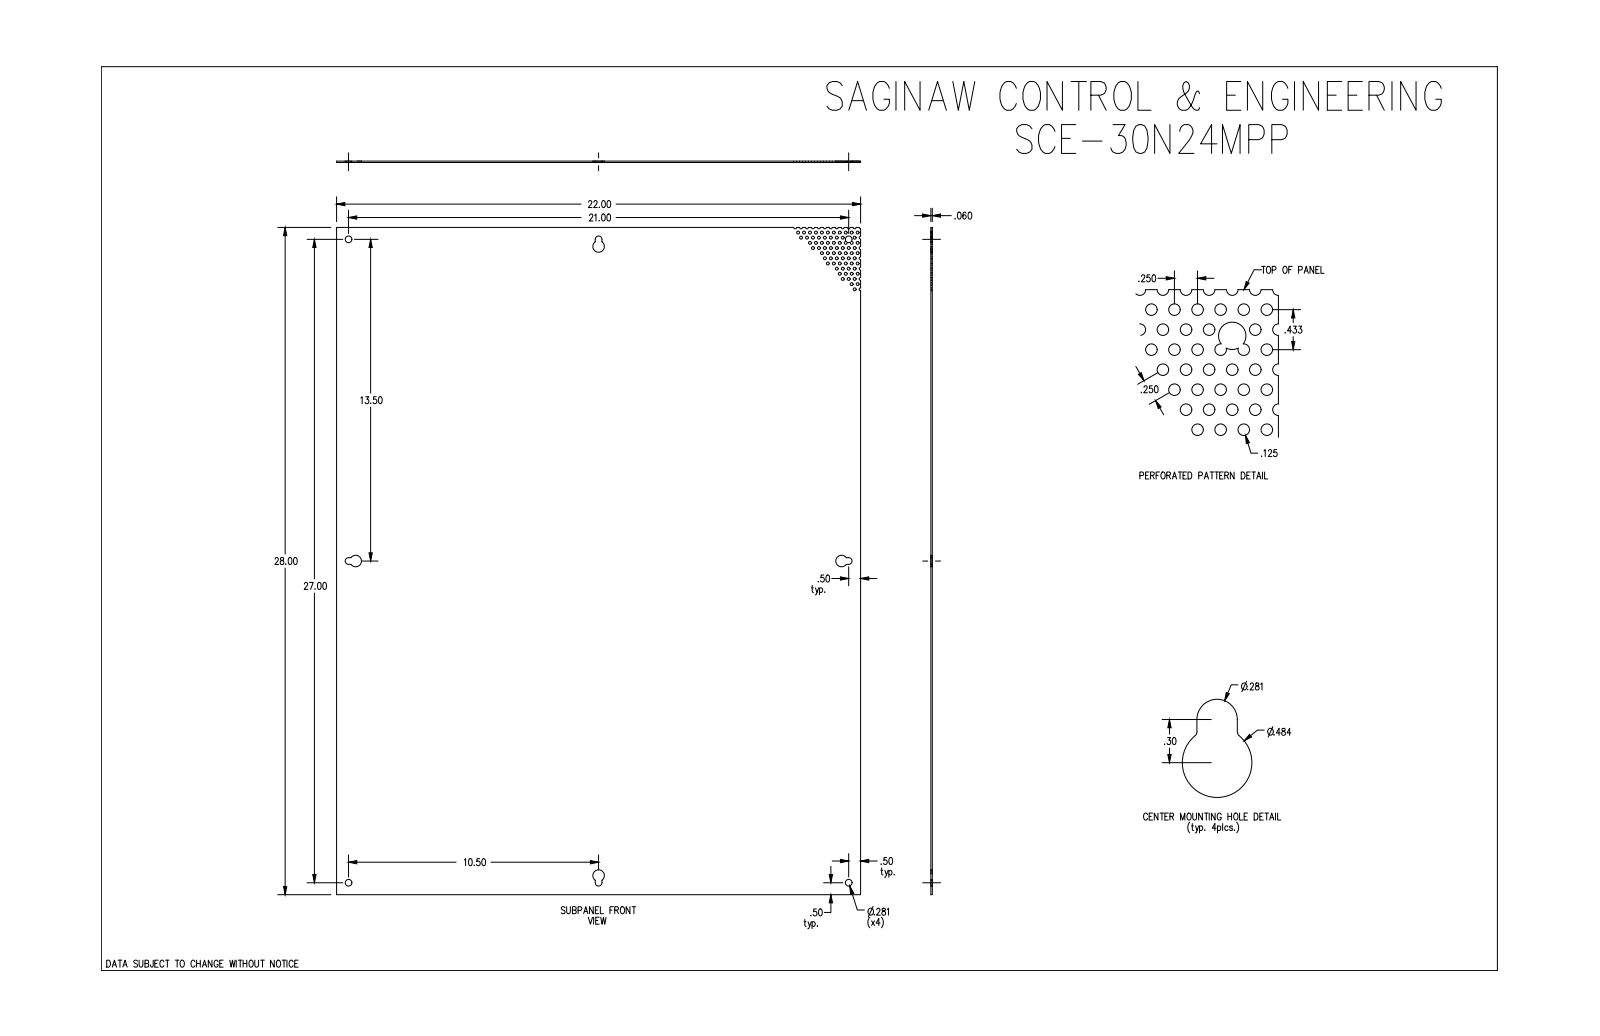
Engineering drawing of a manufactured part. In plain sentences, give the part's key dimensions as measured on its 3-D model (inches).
The part is named "SCE-30N24MPP". Its 3-D file was written by "SolidWorks 2019 (CONFIG_CONTROL_DESIGN)". It is 1 solid with 140 faces: 31 planar, 109 cylindrical and 0 other. Overall it measures 28 by 22 by 0.06 inches. Its volume is 36.83 cubic inches and its surface area 1 236 square inches. Round holes: 45 of diameter 0.125, 25 of diameter 0.125, 4 of diameter 0.281. Partial cylindrical surfaces (rounded edges, fillets, slot ends): 11 of radius 0.063, 8 of radius 0.03, 7 of radius 0.062, 4 of radius 0.141, 4 of radius 0.242. The main face-to-face distances are 0.06, 22, 28, 13.859, 14.141, 0.281, 10.859, 11.141. The hole center spacings are 0.25, 0.661, 0.5, 0.433, 1.323, 0.433, 1.09, 0.75.
